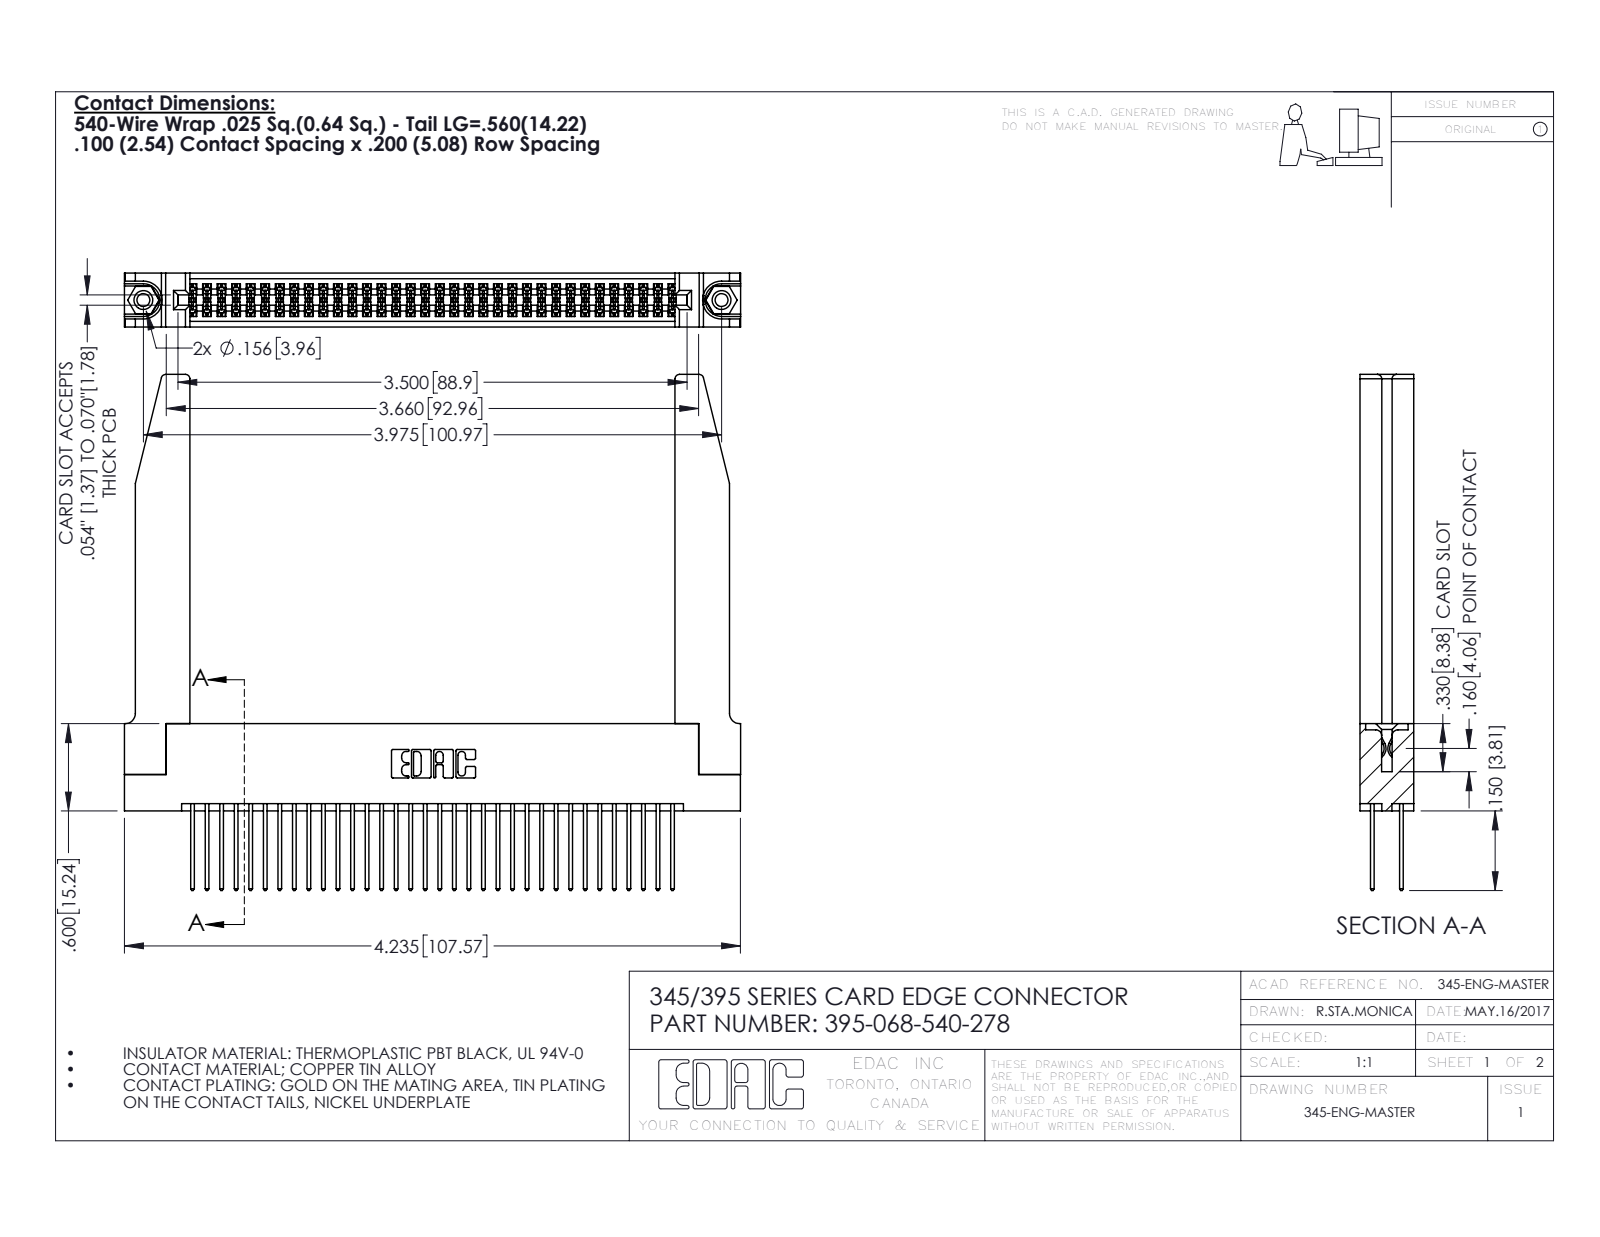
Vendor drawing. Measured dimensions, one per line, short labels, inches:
name: 345-292-001_345-293-140; 345-220-078_345-220-078; 345 Part_Flush Mounting Lugs - 0.156 Dia-TH; 395-068-540-278 (+1 more)
written by: SolidWorks 2016 (CONFIG_CONTROL_DESIGN)
unit: in
bodies: 73 solids, 3760 faces (2466 planar, 1242 cylindrical, 52 other)
size: 4.236 × 3.547 × 0.37
volume: 1.123 in³; area: 36.58 in²
holes: 2× ⌀0.089, 2× ⌀0.125, 2× ⌀0.156, 1× ⌀0.064
bosses: 2× ⌀0.155
rounds: 102× R0.006, 68× R0.01, 22× R0.01, 8× R0.03, 6× R0.007, 6× R0.031, 3× R0.026, 2× R0.014
face distances: 0.072, 0.298, 0.37, 0.2, 0.098, 0.272, 0.025, 0.225, 0.175, 0.15
hole spacings: 0.27, 3.74, 3.975
